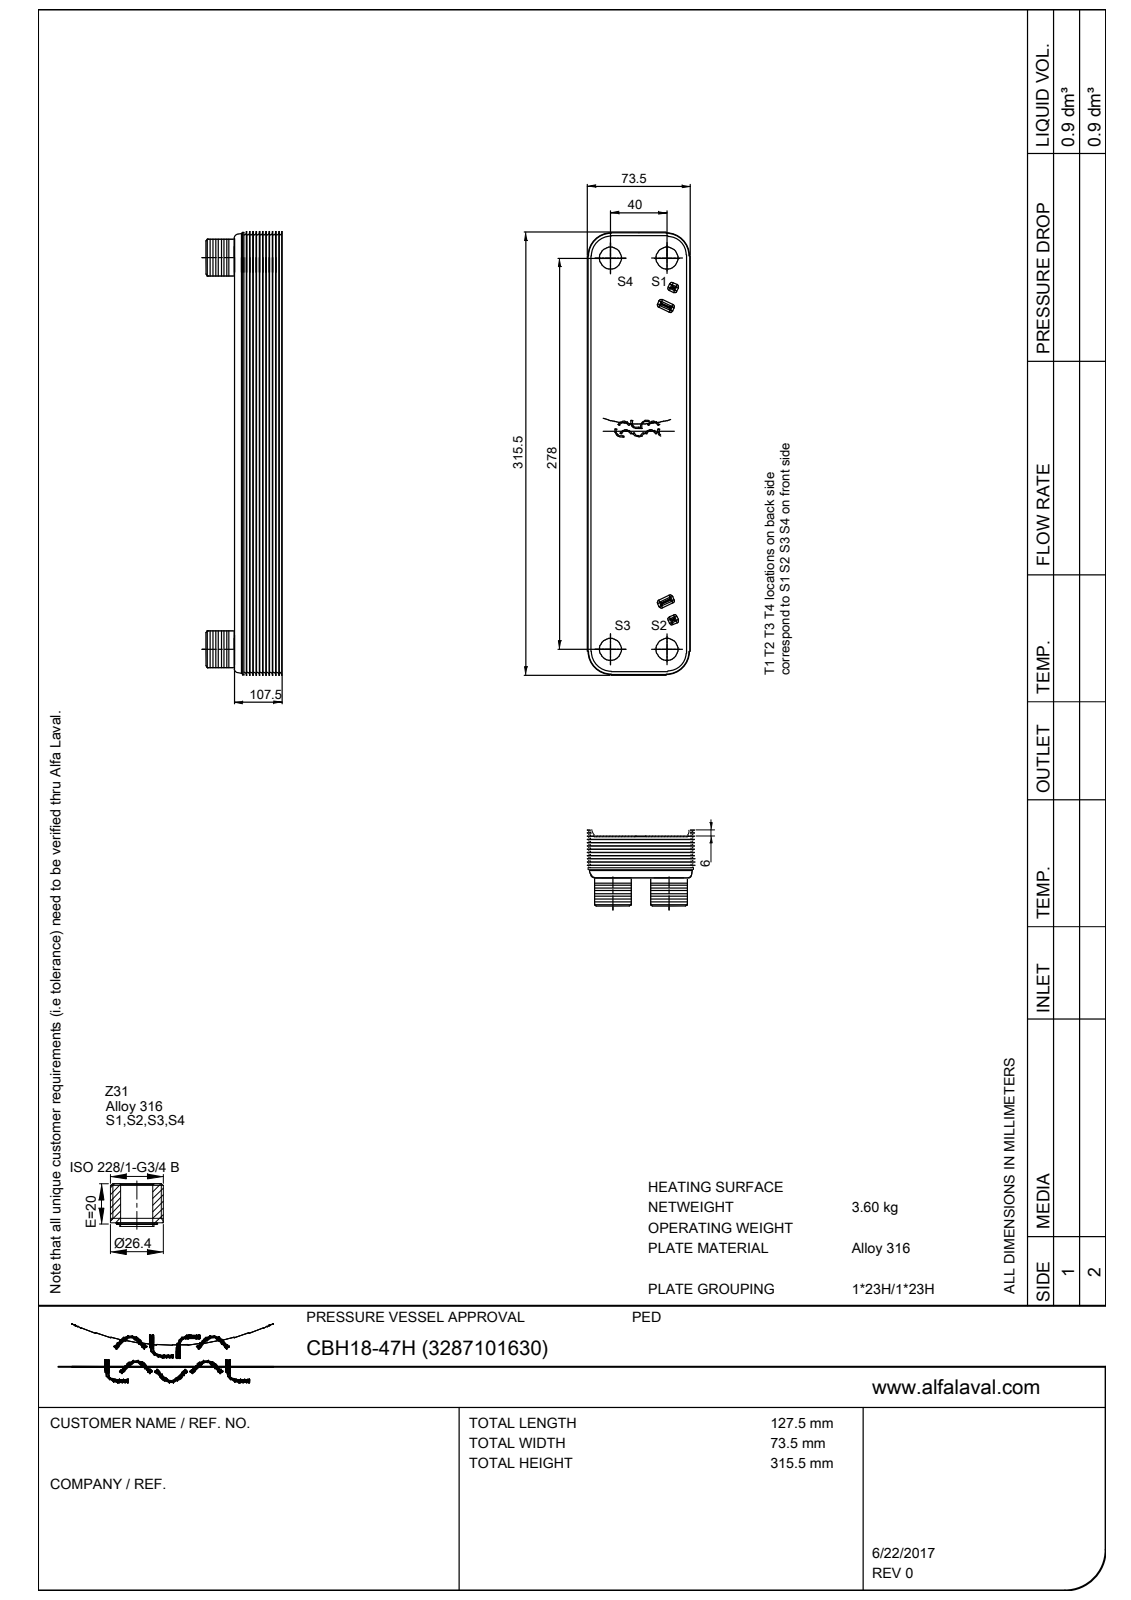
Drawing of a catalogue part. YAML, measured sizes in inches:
part_name: "CBH18_CH_47H; CBH18_FP_S1S2S3S4_16; CBH18_PP; Z31 (+1 more)"
step_written_by: "PRO/ENGINEER BY PARAMETRIC TECHNOLOGY CORPORATION, 2007390 (CONFIG_CONTROL_DESIGN)"
units: inches
bodies: {solids: 7, faces: 480, planar: 128, cylindrical: 144, other: 208}
overall_size: [12.559, 5.098, 3.051]
volume: 150.5
surface_area: 421.4
round_holes:
  - {diameter: 0.63, count: 4}
  - {diameter: 0.659, count: 4}
  - {diameter: 0.807, count: 4}
round_bosses_or_shafts:
  - {diameter: 1.041, count: 4}
  - {diameter: 0.709, count: 4}
partial_cylinders:
  - {radius: 0.039, count: 18}
  - {radius: 0.016, count: 16}
  - {radius: 0.028, count: 16}
  - {radius: 0.055, count: 16}
  - {radius: 0.067, count: 16}
  - {radius: 0.02, count: 4}
  - {radius: 0.059, count: 4}
  - {radius: 0.787, count: 4}
face_to_face_distances: [0.039, 4.047, 4.008, 3.051, 4.087, 0.565, 12.559, 0.041, 0.045, 4.093]
hole_center_spacings: [1.575, 10.945, 11.057]
